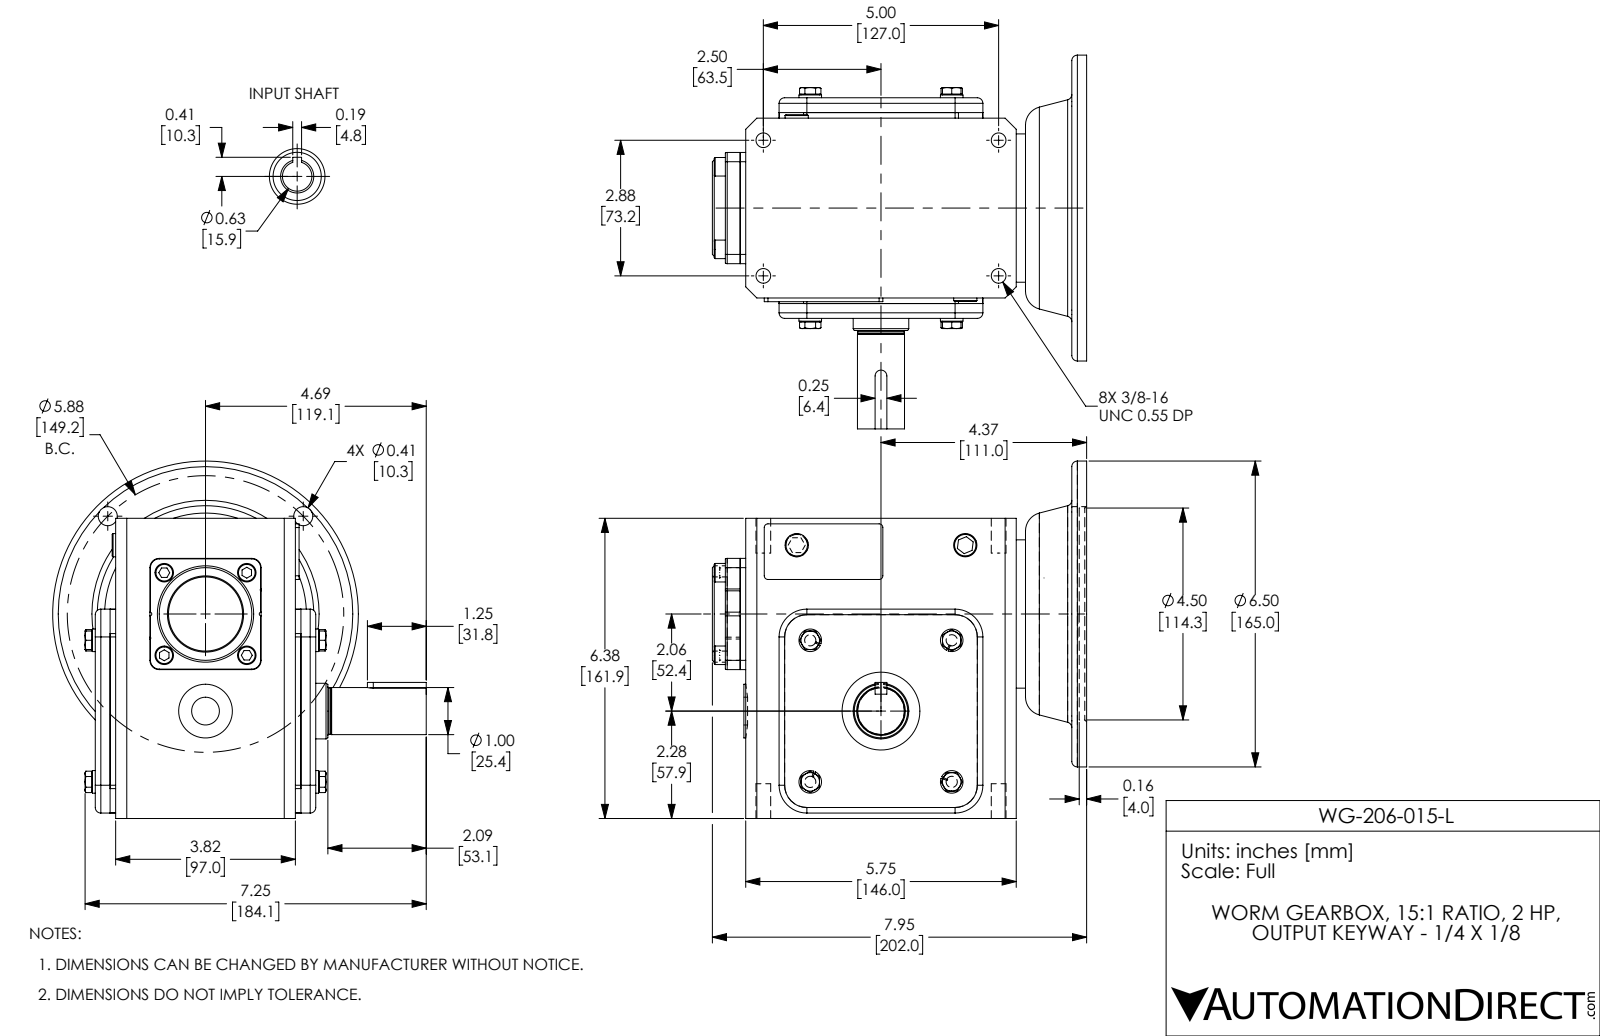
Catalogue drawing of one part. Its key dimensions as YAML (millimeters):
part_name: "WG-206-015-L"
step_written_by: "SolidWorks 2017 (AUTOMOTIVE_DESIGN)"
units: millimeters
bodies: {solids: 44, faces: 619, planar: 303, cylindrical: 188, other: 128}
overall_size: [202, 201.6, 192.8]
volume: 2776000
surface_area: 269800
round_holes:
  - {diameter: 8, count: 4}
  - {diameter: 10.3, count: 4}
  - {diameter: 12.6, count: 2}
  - {diameter: 30, count: 2}
  - {diameter: 15, count: 1}
  - {diameter: 15.9, count: 1}
  - {diameter: 37, count: 1}
  - {diameter: 42, count: 1}
  - {diameter: 90, count: 1}
  - {diameter: 114.3, count: 1}
round_bosses_or_shafts:
  - {diameter: 10, count: 8}
  - {diameter: 12.2, count: 4}
  - {diameter: 165, count: 1}
  - {diameter: 80, count: 1}
  - {diameter: 52, count: 1}
  - {diameter: 40, count: 1}
  - {diameter: 29, count: 1}
  - {diameter: 25.4, count: 1}
partial_cylinders:
  - {radius: 2, count: 8}
  - {radius: 3, count: 8}
  - {radius: 5, count: 4}
  - {radius: 15, count: 4}
  - {radius: 0.5, count: 2}
  - {radius: 1, count: 2}
  - {radius: 3.2, count: 1}
  - {radius: 69, count: 1}
face_to_face_distances: [8, 3, 103, 111, 11, 100, 108, 161.9, 119, 18]
hole_center_spacings: [74.6, 105.5, 52.8, 68.1, 73.2, 117.6, 127, 146.6]
